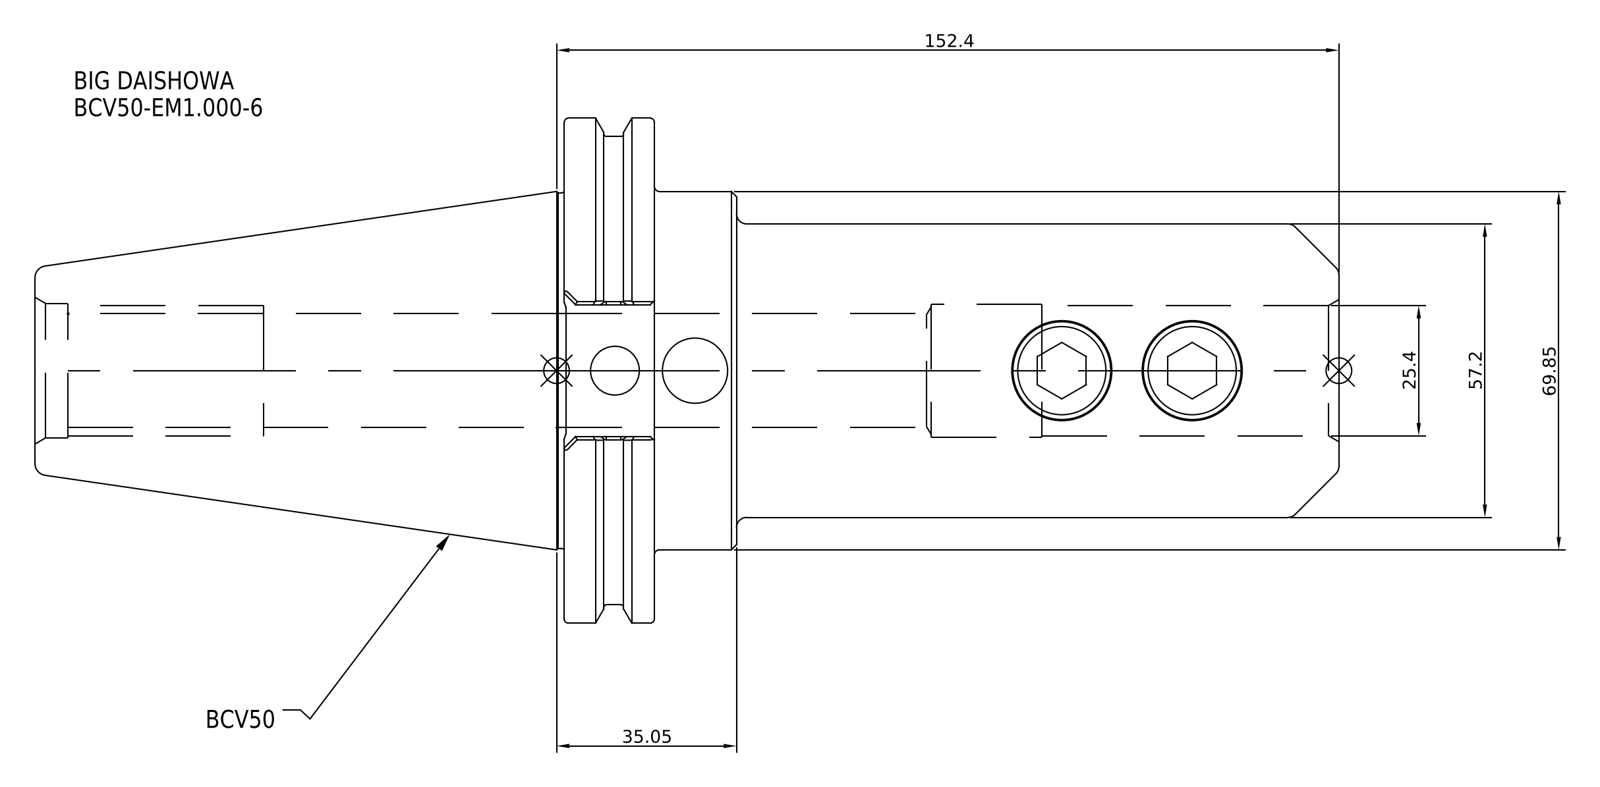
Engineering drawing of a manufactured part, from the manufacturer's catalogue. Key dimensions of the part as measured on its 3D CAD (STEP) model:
Part name (STEP PRODUCT): BCV50-EM1_000-6
STEP written by: SolidWorks 2021 (CONFIG_CONTROL_DESIGN)
Units: millimetres
Bodies: 1 solid, 30 faces (8 planar, 14 cylindrical, 8 other)
Overall size (bounding box): 254 × 98.43 × 98.43
Volume: 678 113 mm³ · Surface area: 70 370 mm²
Round holes (diameter × count): ⌀25.4 ×1
Round bosses / shafts (diameter × count): ⌀98.43 ×1, ⌀91.29 ×1, ⌀69.85 ×1, ⌀57.2 ×1
Main face-to-face distances: 17.55, 16, 33.55, 136.65, 120.65, 103.1, 117.35, 133.35, 150.9, 254
